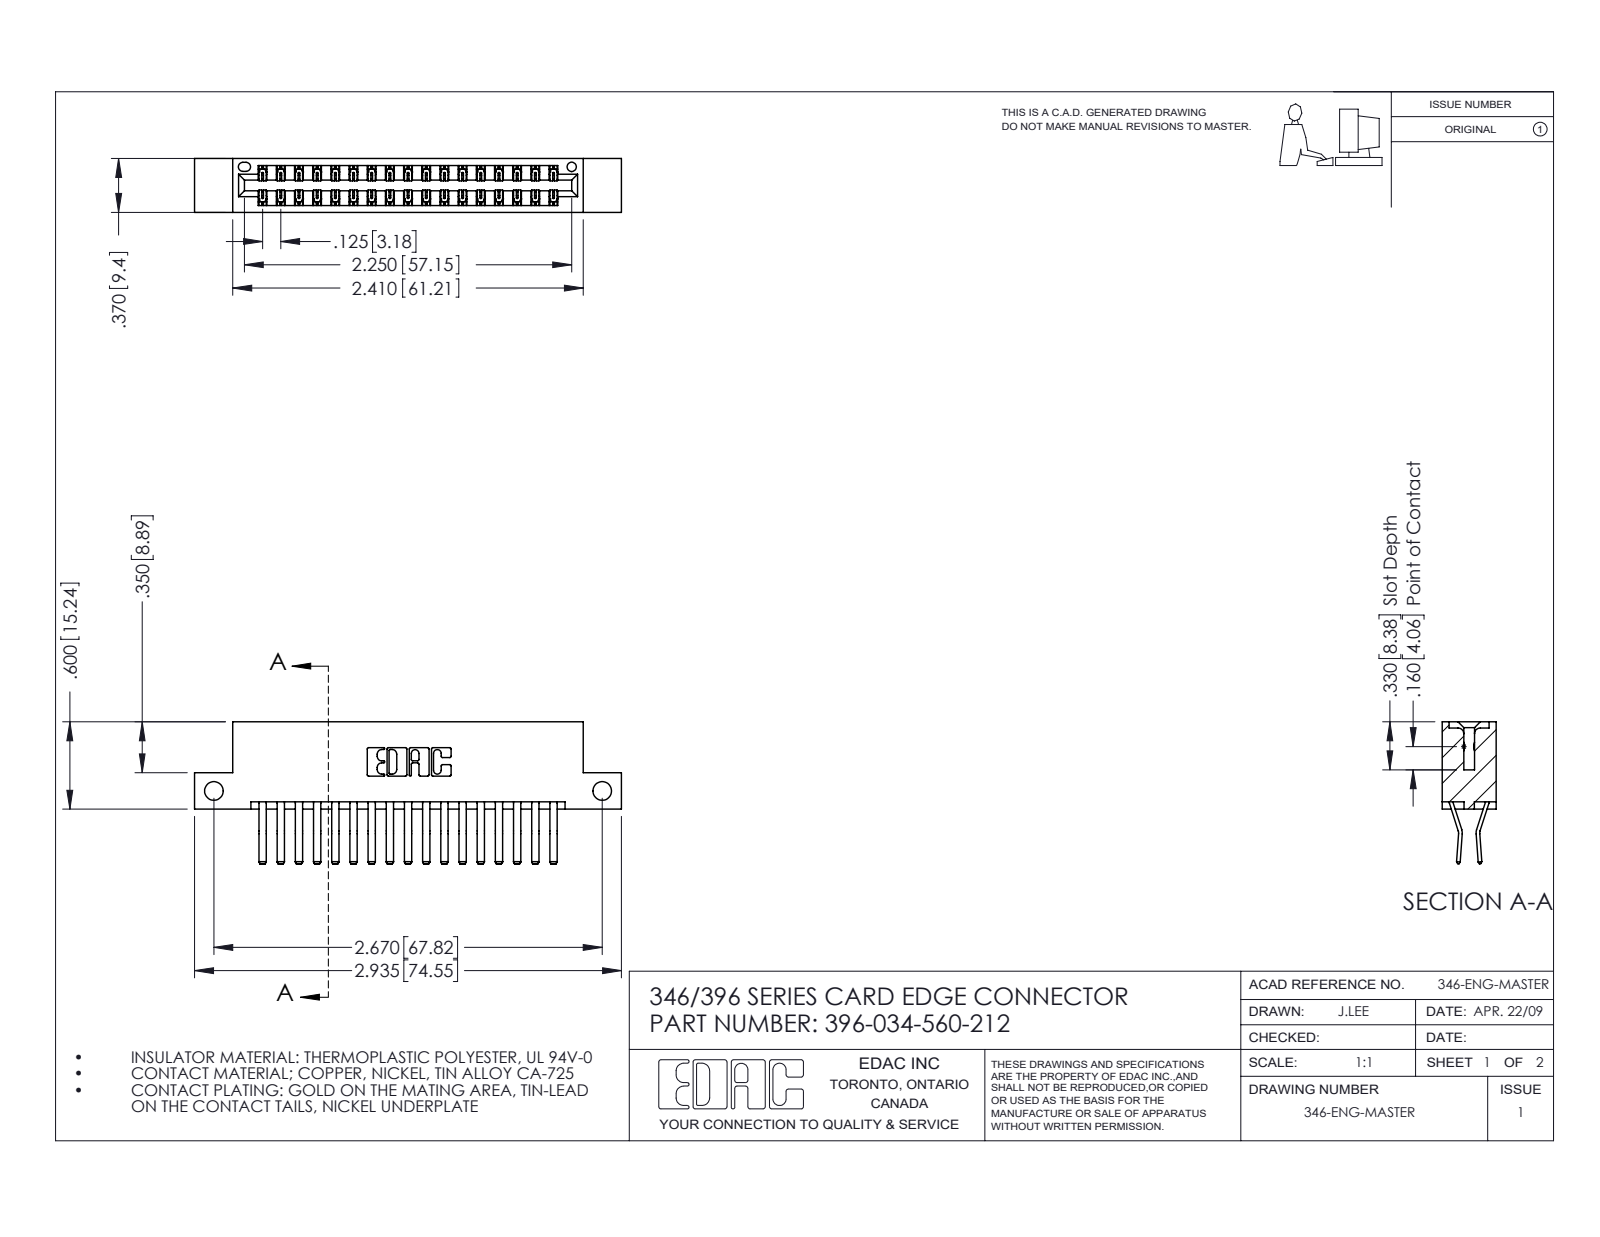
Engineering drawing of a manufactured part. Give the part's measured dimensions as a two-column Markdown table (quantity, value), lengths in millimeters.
| quantity | value |
| --- | --- |
| part name | 346 Part_Flush Mounting Lugs - Side Mount; 396-034-560-212; 345-292-001_560 Tail |
| STEP written by | SolidWorks 2016 (CONFIG_CONTROL_DESIGN) |
| units | millimeters |
| bodies | 35 solids, 1958 faces (1266 planar, 692 cylindrical, 0 other) |
| overall size | 74.5 × 24.8 × 9.4 |
| volume | 7 210 mm³ |
| surface area | 9 974 mm² |
| round holes (diameter × count) | 3.3 × 2, 1.6 × 1 |
| partial cylindrical surfaces (radius × count) | 0.2 × 51, 0.3 × 22, 0.2 × 6, 0.8 × 6, 0.7 × 3, 0.3 × 2, 0.4 × 2, 0.6 × 2 |
| main face-to-face distances | 1.2, 8.2, 6.4, 9.4, 0.6, 1.8, 7.6, 7, 3.8, 5.6 |
| hole center spacings | 67.8 |
